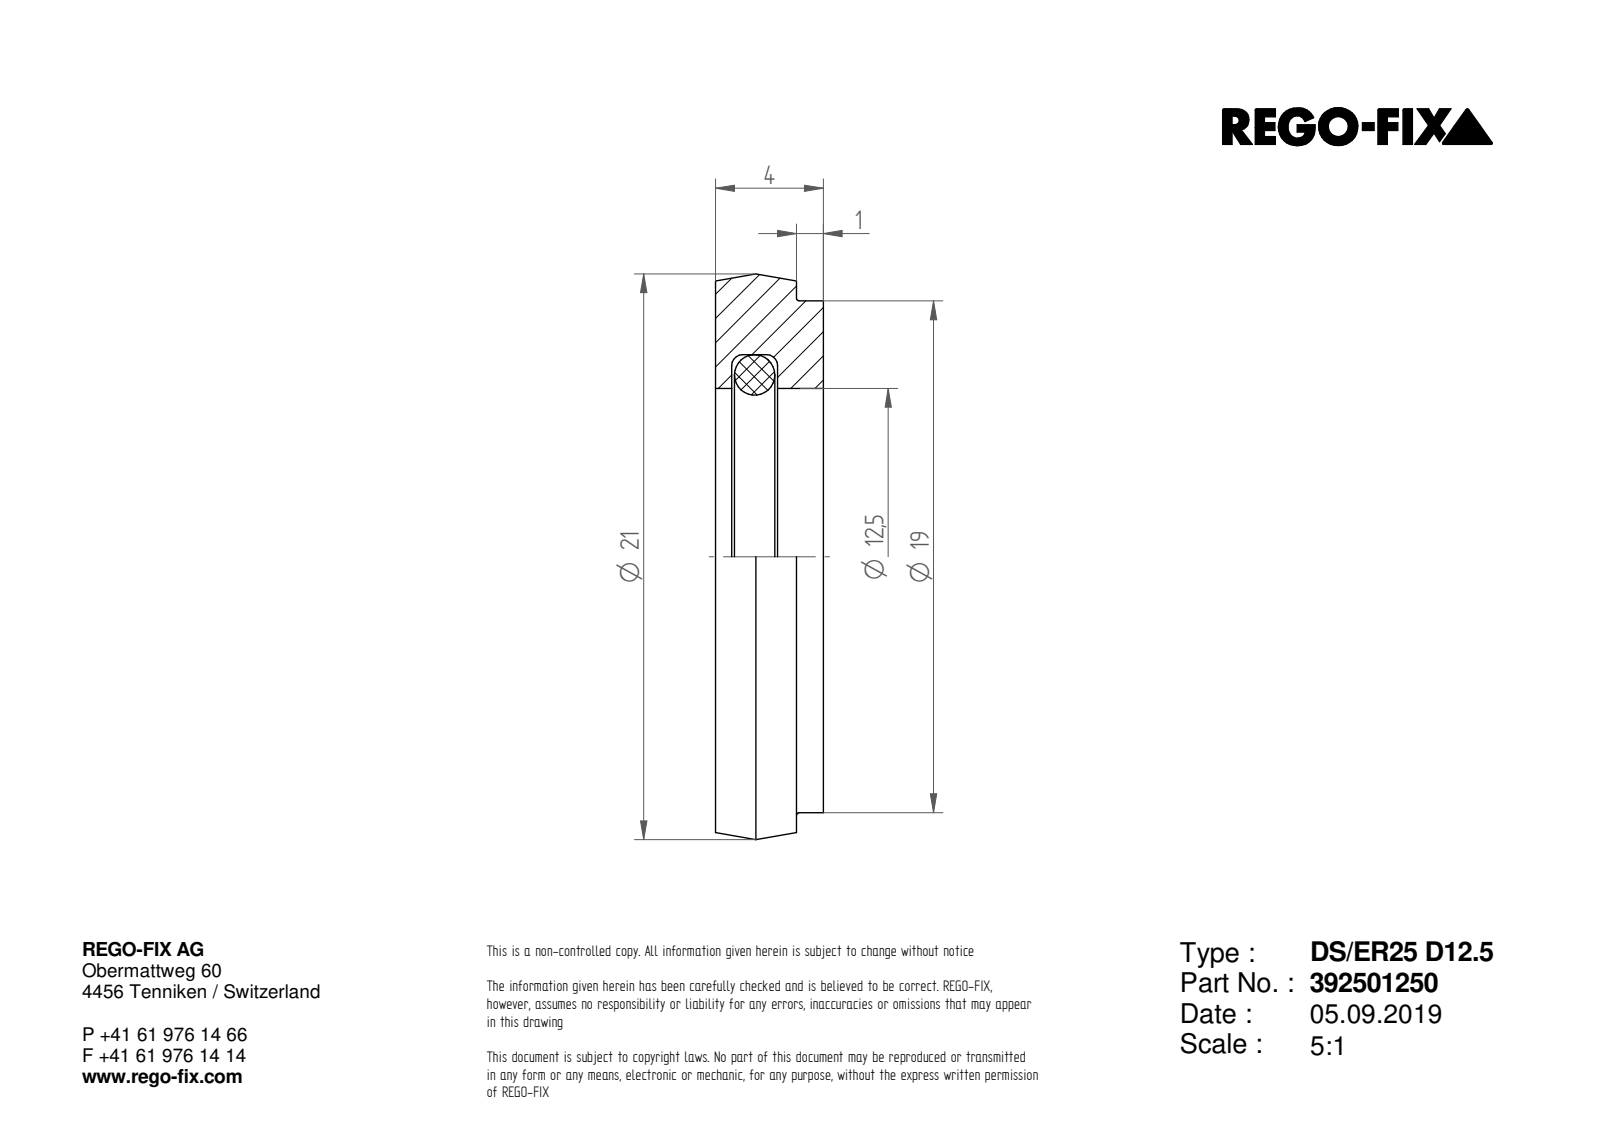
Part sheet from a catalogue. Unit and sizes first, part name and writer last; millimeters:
Units: millimetres
Overall size (bounding box): 21 × 21 × 4
Round holes (diameter × count): ⌀12.5 ×1
Round bosses / shafts (diameter × count): ⌀21 ×1, ⌀19 ×1
Main face-to-face distances: 4, 1, 3
Volume: 832 mm³ · Surface area: 859 mm²
Bodies: 1 solid, 7 faces (3 planar, 3 cylindrical, 1 other)
Part name (STEP PRODUCT): NOCUT
STEP written by: SIEMENS PLM Software Solid Edge ST10 (AUTOMOTIVE_DESIGN)
